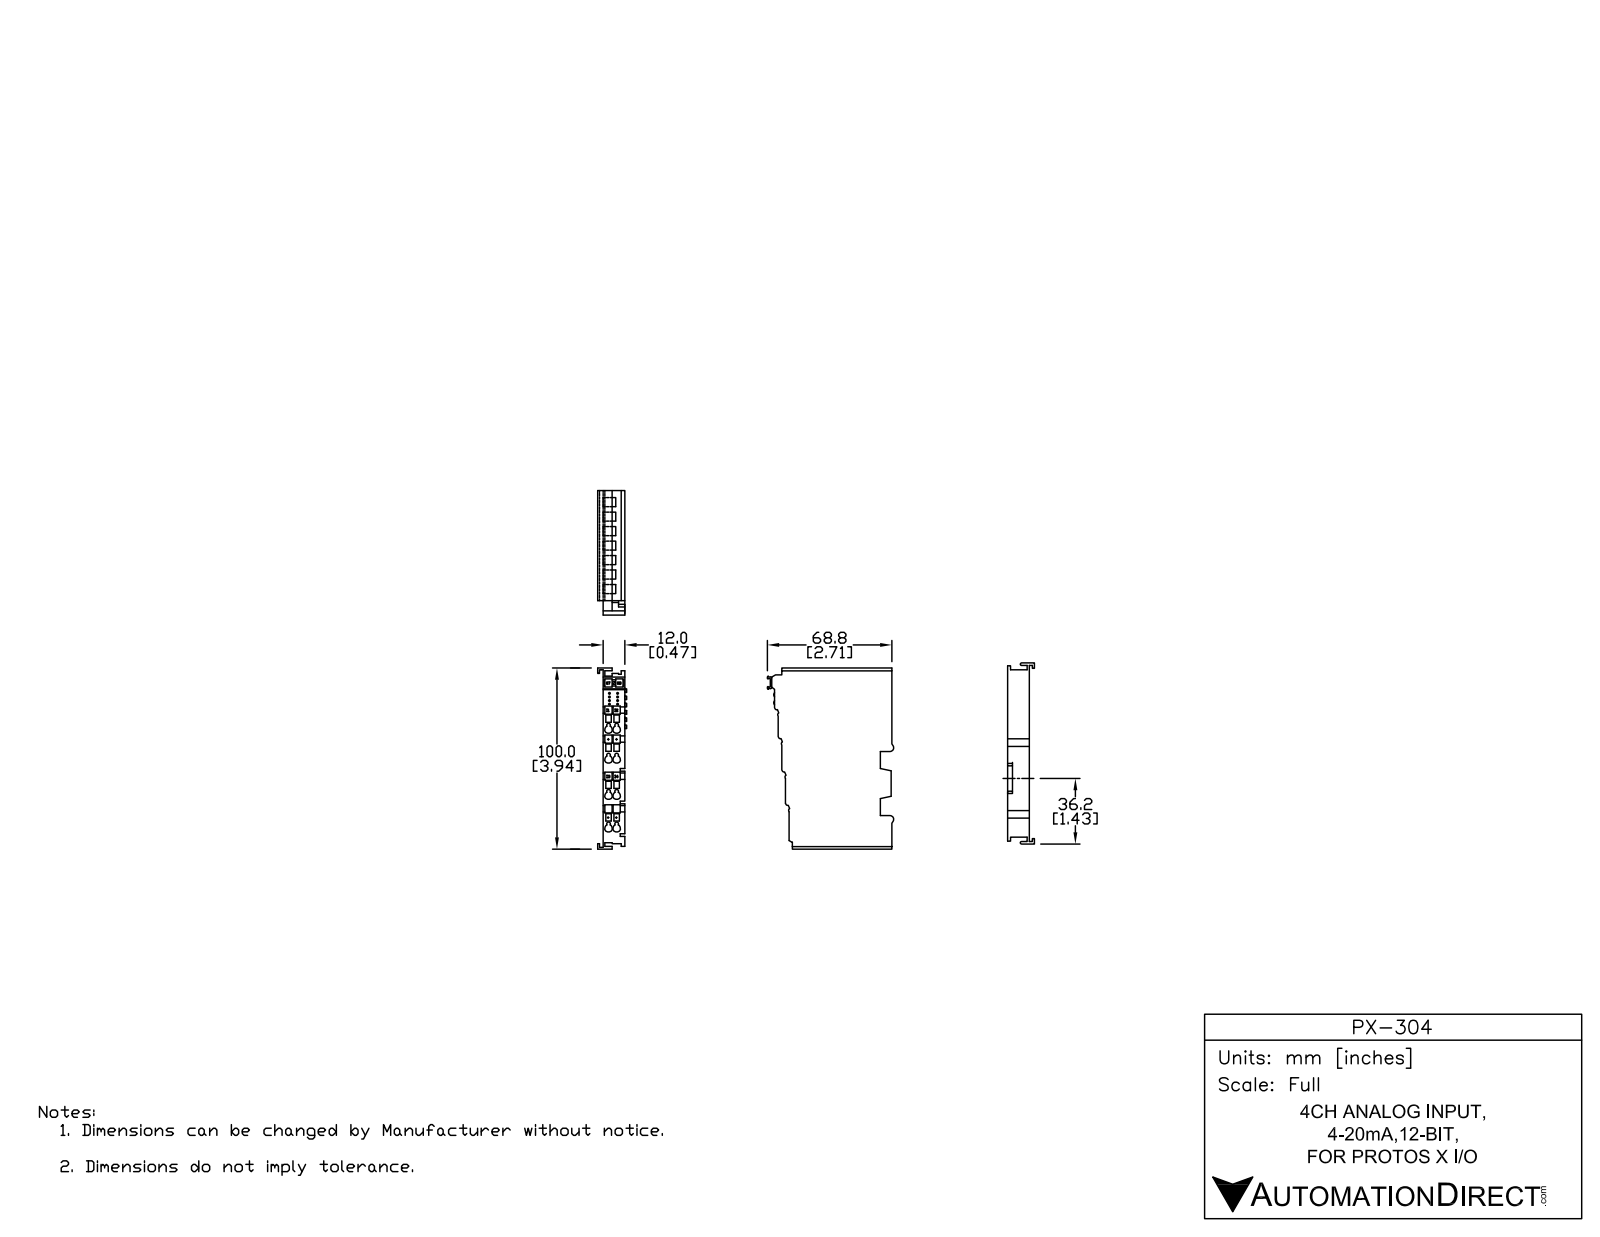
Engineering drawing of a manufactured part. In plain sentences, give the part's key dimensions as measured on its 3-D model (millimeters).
The part is named "PX-304". Its 3-D file was written by "SolidWorks 2014 (AUTOMOTIVE_DESIGN)". It is 26 solids with 1425 faces: 1011 planar, 354 cylindrical and 60 other. Overall it measures 100.25 by 69.28 by 15.15 millimeters. Its volume is 59 090 cubic millimeters and its surface area 32 341 square millimeters. Round holes: 8 of diameter 4. Partial cylindrical surfaces (rounded edges, fillets, slot ends): 67 of radius 0.25, 43 of radius 0.3, 12 of radius 0.38, 10 of radius 0.4, 8 of radius 1, 4 of radius 0.17, 4 of radius 1.03, 4 of radius 1.38. The main face-to-face distances are 12, 2, 10, 1, 1.85, 11, 4, 8.7, 3.15, 1.22. The hole center spacings are 5, 18.4, 19.07, 16, 16.76, 34.4, 34.76, 36.8.
